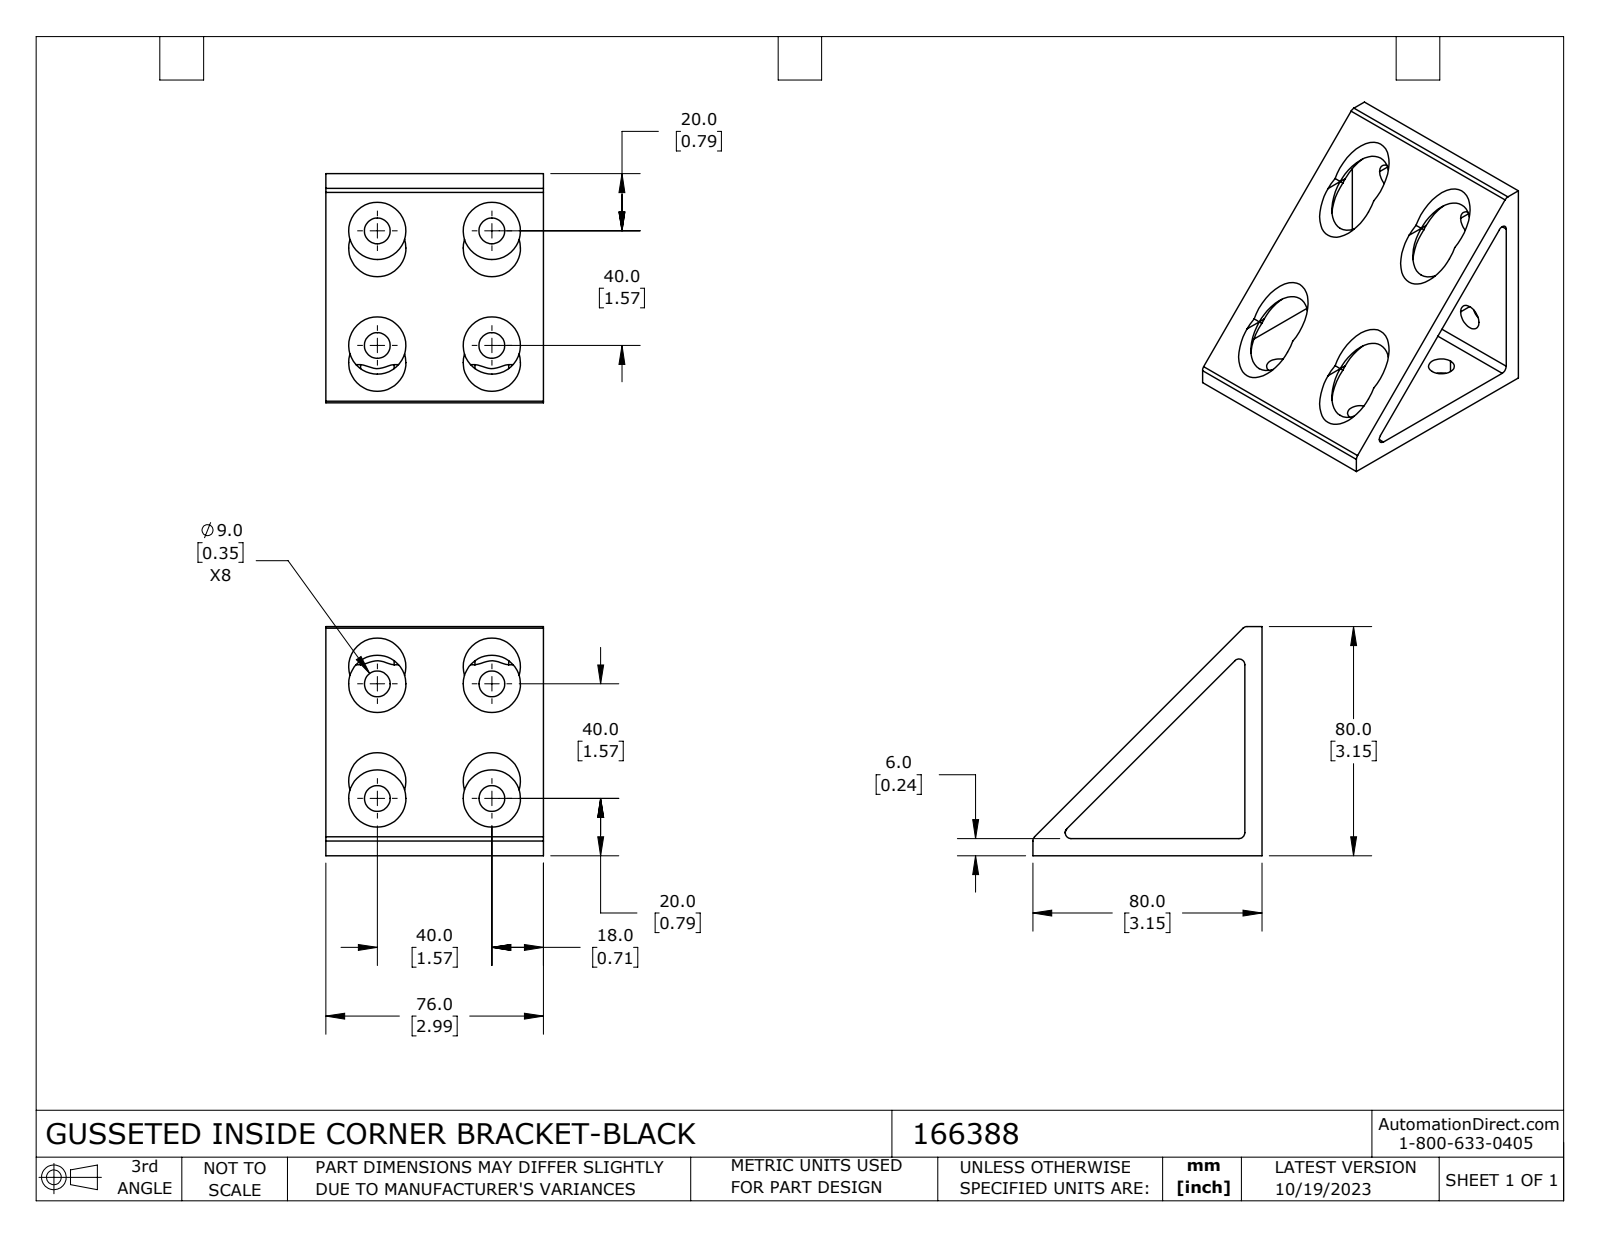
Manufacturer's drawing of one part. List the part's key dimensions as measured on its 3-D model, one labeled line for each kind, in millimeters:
Part name (STEP PRODUCT): 166388
STEP written by: SolidWorks 2023 (CONFIG_CONTROL_DESIGN)
Units: millimetres
Bodies: 1 solid, 78 faces (10 planar, 64 cylindrical, 4 other)
Overall size (bounding box): 80 × 80 × 76
Volume: 100 478 mm³ · Surface area: 38 432 mm²
Round holes (diameter × count): ⌀9 ×8, ⌀20 ×8
Partial cylindrical surfaces — rounded edges, fillets, slot ends (radius × count): R2 ×5
Main face-to-face distances: 6, 76, 80, 74
Hole centre spacings: 40, 56.57
